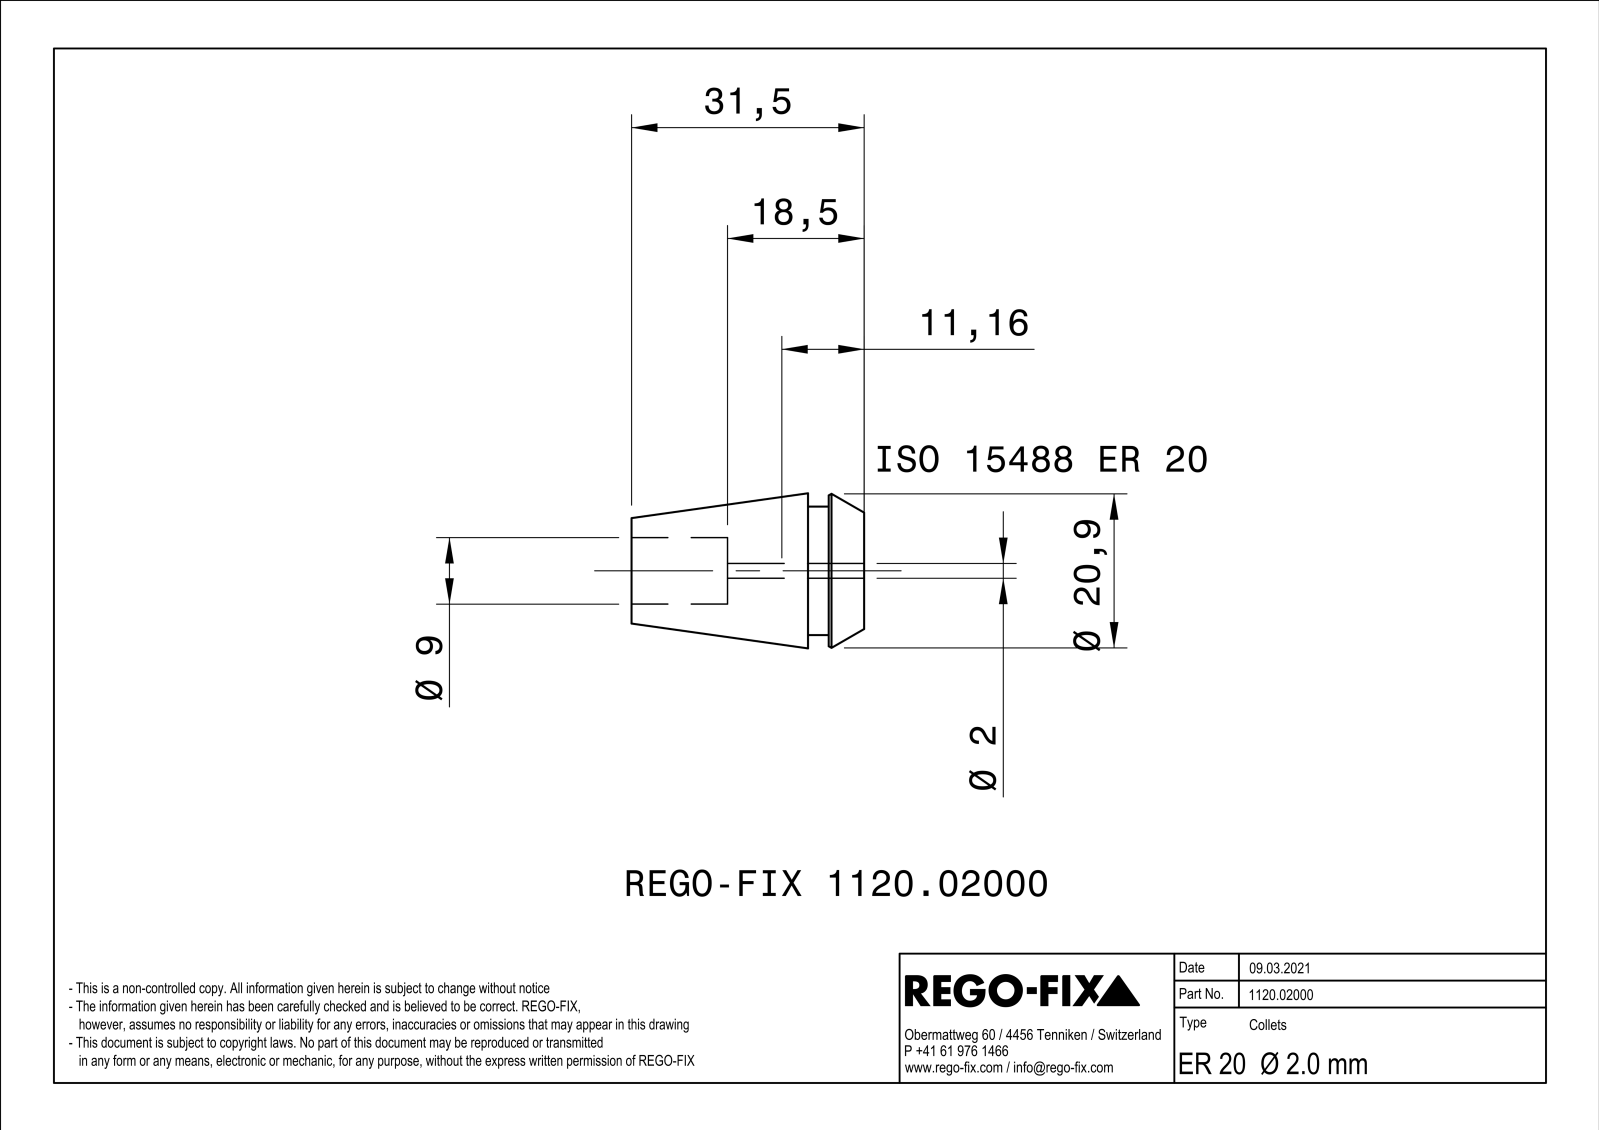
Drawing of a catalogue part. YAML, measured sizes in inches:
part_name: "NOCUT"
step_written_by: "SIEMENS PLM Software Solid Edge ST10 (AUTOMOTIVE_DESIGN)"
units: inches
bodies: {solids: 1, faces: 264, planar: 104, cylindrical: 48, other: 112}
overall_size: [1.24, 0.827, 0.827]
volume: 0.364
surface_area: 10.79
round_holes:
  - {diameter: 0.354, count: 1}
round_bosses_or_shafts:
  - {diameter: 0.685, count: 1}
partial_cylinders:
  - {radius: 1.378, count: 8}
  - {radius: 0.039, count: 1}
face_to_face_distances: [0.018, 0.017, 0.018, 0.299, 0.189, 0.11, 1.24, 1.051, 0.941, 0.728]
